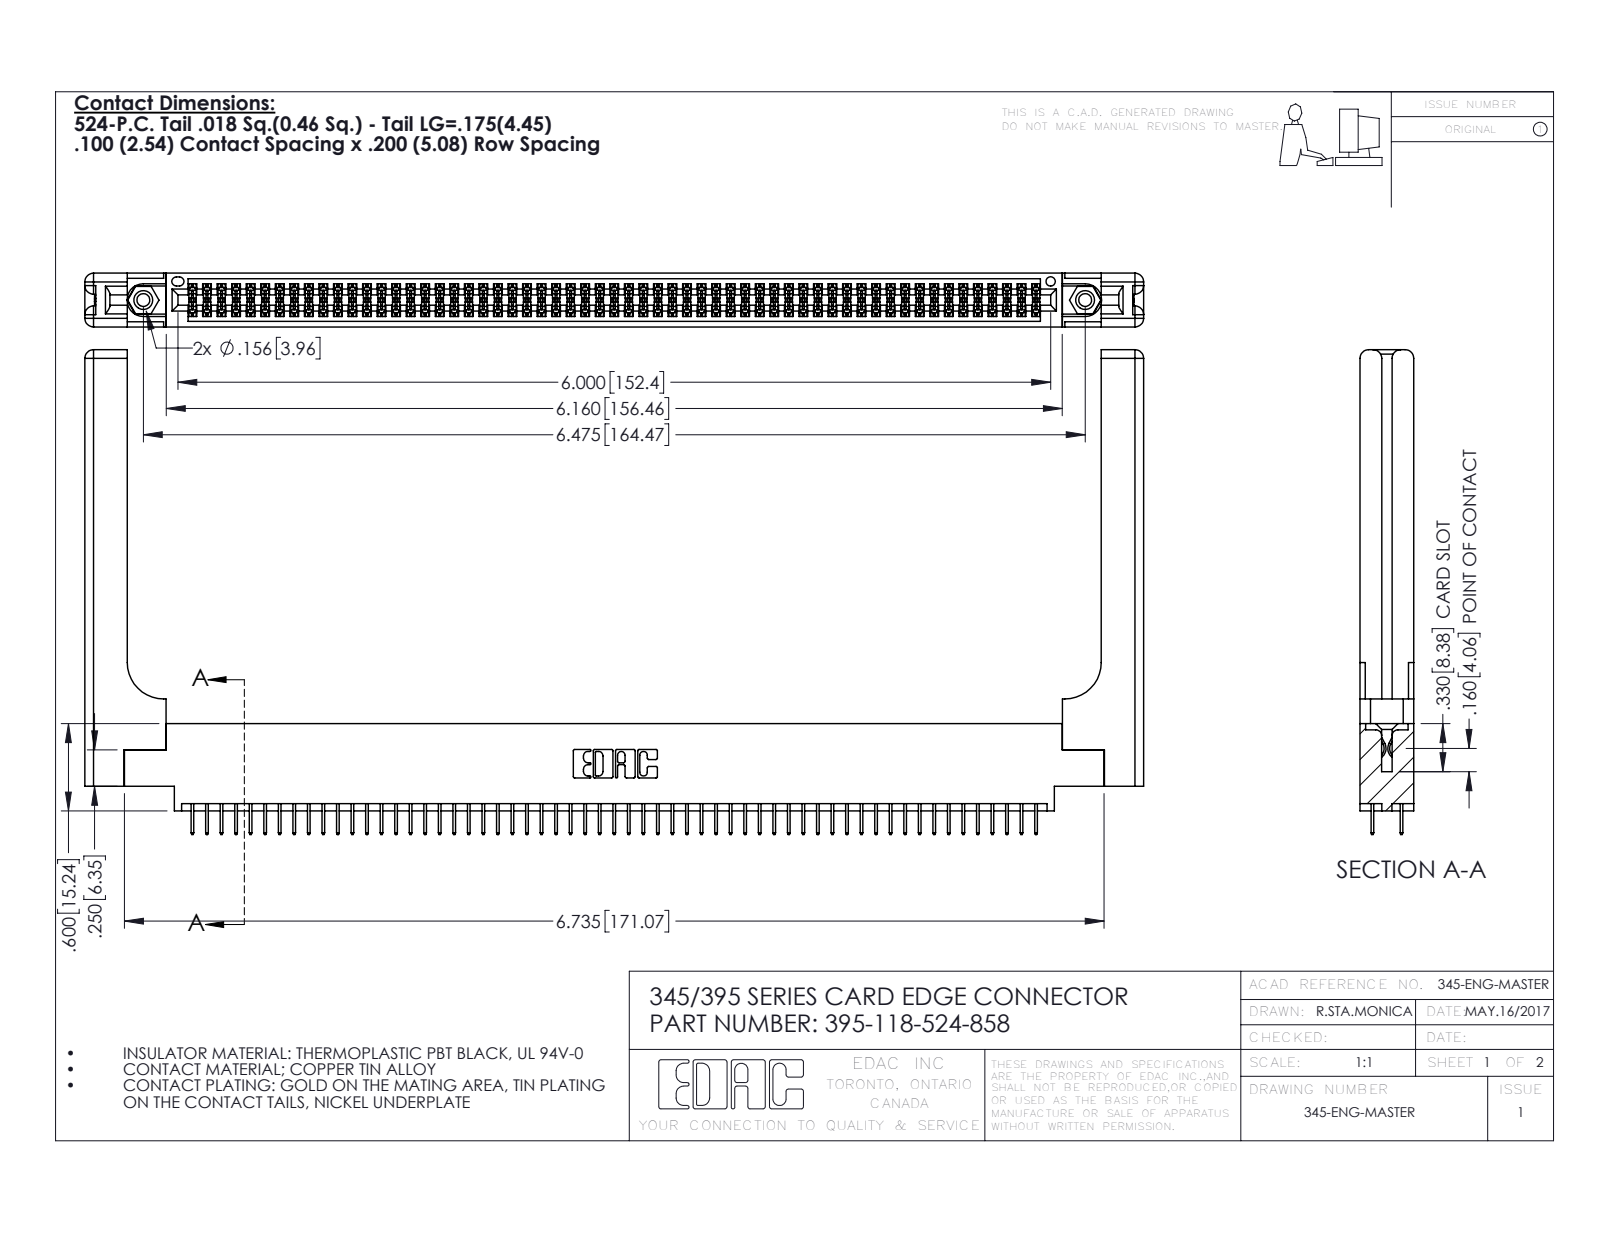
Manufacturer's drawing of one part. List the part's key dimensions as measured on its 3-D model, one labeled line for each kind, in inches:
Part name (STEP PRODUCT): 345 Part_0.170 Offset - 0.156 Dia-TH; 395-118-524-858; 345-292-001_345-293-124; 345-220-058_345-220-058 (+1 more)
STEP written by: SolidWorks 2016 (CONFIG_CONTROL_DESIGN)
Units: inches
Bodies: 123 solids, 6758 faces (4834 planar, 1864 cylindrical, 60 other)
Overall size (bounding box): 7.279 × 3.332 × 0.37
Volume: 1.605 in³ · Surface area: 48.69 in²
Round holes (diameter × count): ⌀0.089 ×2, ⌀0.125 ×2, ⌀0.156 ×2, ⌀0.064 ×1
Round bosses / shafts (diameter × count): ⌀0.155 ×2
Partial cylindrical surfaces — rounded edges, fillets, slot ends (radius × count): R0.006 ×177, R0.01 ×22, R0.06 ×16, R0.007 ×6, R0.031 ×6, R0.026 ×3, R0.014 ×2, R0.019 ×2
Main face-to-face distances: 0.072, 0.37, 0.298, 0.2, 0.098, 0.272, 0.025, 0.225, 0.175, 0.148
Hole centre spacings: 0.27, 6.239, 6.475
